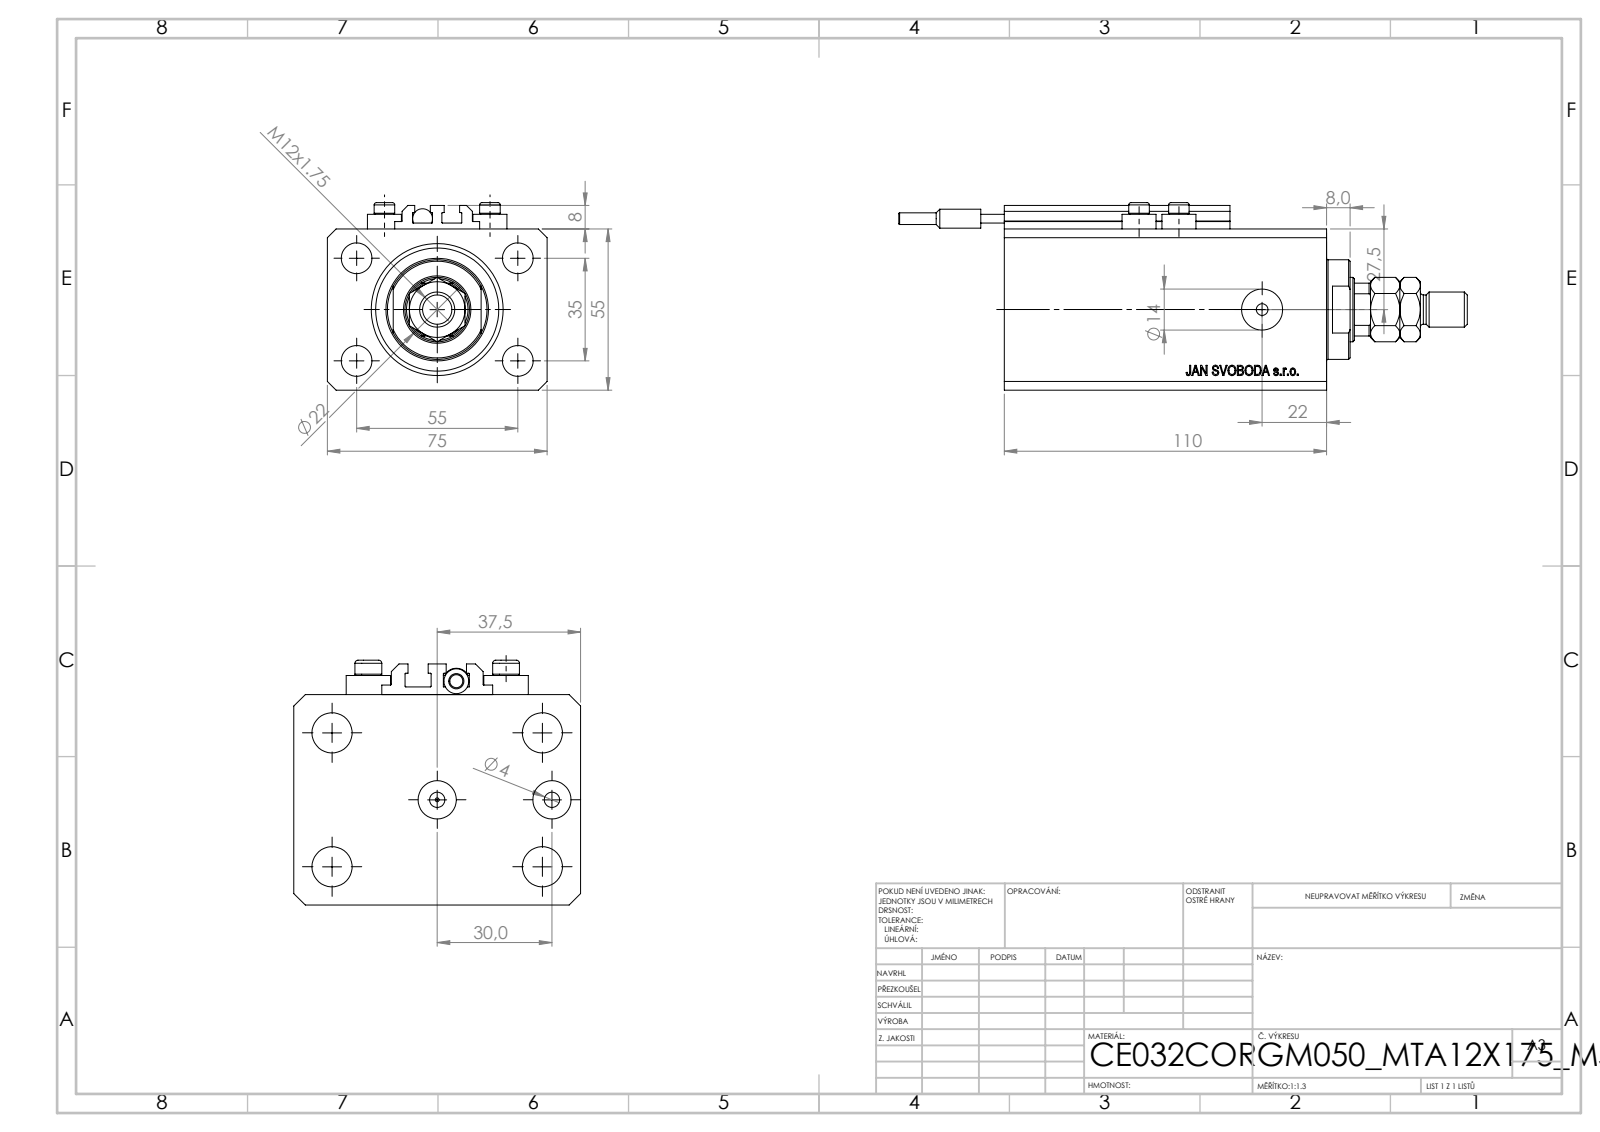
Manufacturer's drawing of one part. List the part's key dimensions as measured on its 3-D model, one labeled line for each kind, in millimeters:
Part name (STEP PRODUCT): MTA; V250CE_C_VCP; V250CE_VC_C; ALLEN BOLT V250CE (+2 more)
STEP written by: SolidWorks 2019 (CONFIG_CONTROL_DESIGN)
Units: millimetres
Bodies: 10 solids, 1113 faces (535 planar, 98 cylindrical, 480 other)
Overall size (bounding box): 194 × 75 × 64
Volume: 417 208 mm³ · Surface area: 95 300 mm²
Round holes (diameter × count): ⌀4 ×8, ⌀10.5 ×5, ⌀10 ×2, ⌀14 ×2, ⌀1.25 ×1, ⌀22 ×1, ⌀32 ×1, ⌀45 ×1
Round bosses / shafts (diameter × count): ⌀11.6 ×4, ⌀7 ×4, ⌀34 ×1, ⌀12 ×1, ⌀6.8 ×1, ⌀6.5 ×1, ⌀4 ×1
Partial cylindrical surfaces — rounded edges, fillets, slot ends (radius × count): R0.2 ×10, R10.5 ×1
Main face-to-face distances: 55, 75, 110, 15, 95, 9.9, 85.1, 100.1, 2.5, 3
Hole centre spacings: 32.6, 13.6, 17.68, 35, 36, 38.48, 55, 60.1
